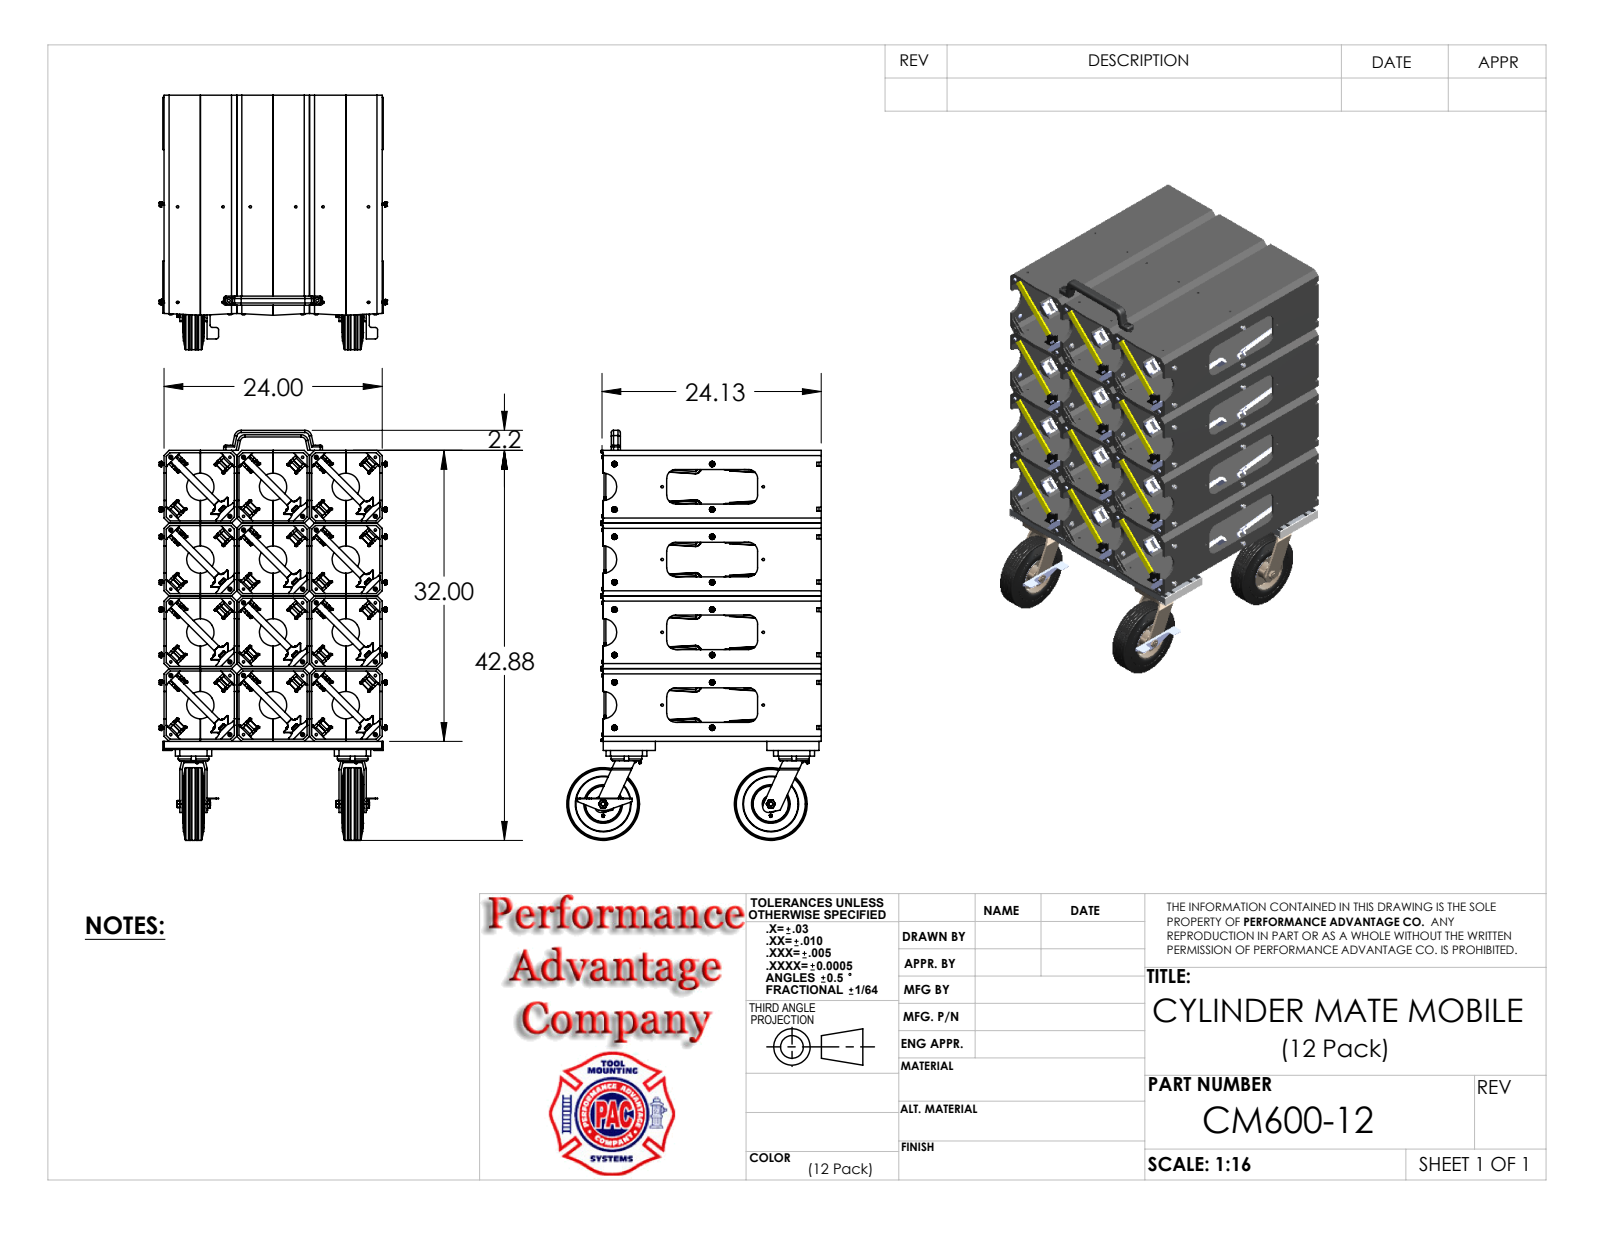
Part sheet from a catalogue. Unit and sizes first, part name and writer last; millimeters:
Units: millimetres
Overall size (bounding box): 1145.4 × 711 × 635
Round holes (diameter × count): ⌀6.8 ×52, ⌀6.6 ×48, ⌀5.1 ×16, ⌀8.7 ×2, ⌀12.7 ×2, ⌀15.9 ×2, ⌀17.4 ×2, ⌀18.6 ×2, ⌀19.1 ×2, ⌀28.6 ×2, ⌀30.2 ×2, ⌀101.6 ×2
Round bosses / shafts (diameter × count): ⌀11.1 ×24, ⌀6.4 ×24, ⌀14.9 ×16, ⌀76.2 ×12, ⌀86.4 ×4, ⌀53.3 ×4, ⌀25.4 ×4, ⌀7.9 ×4
Partial cylindrical surfaces — rounded edges, fillets, slot ends (radius × count): R2.4 ×1164, R0.4 ×956, R0.8 ×209, R7.5 ×192, R11.5 ×192, R1.6 ×122, R3.2 ×108, R2.5 ×96
Main face-to-face distances: 203.2, 6.4, 406.4, 196.9, 209.6, 400.1, 190.5, 609.6, 603.3, 412.8
Hole centre spacings: 203.2, 406.4, 165.1, 454.4, 261.8, 438.7, 127, 233.5
Volume: 59 550 000 mm³ · Surface area: 15 570 000 mm²
Bodies: 447 solids, 21488 faces (7578 planar, 5766 cylindrical, 8144 other)
Part name (STEP PRODUCT): CM6000-12; CM6000; CM6000P; CM6000P - BOX (+8 more)
STEP written by: SolidWorks 2010 (CONFIG_CONTROL_DESIGN)
